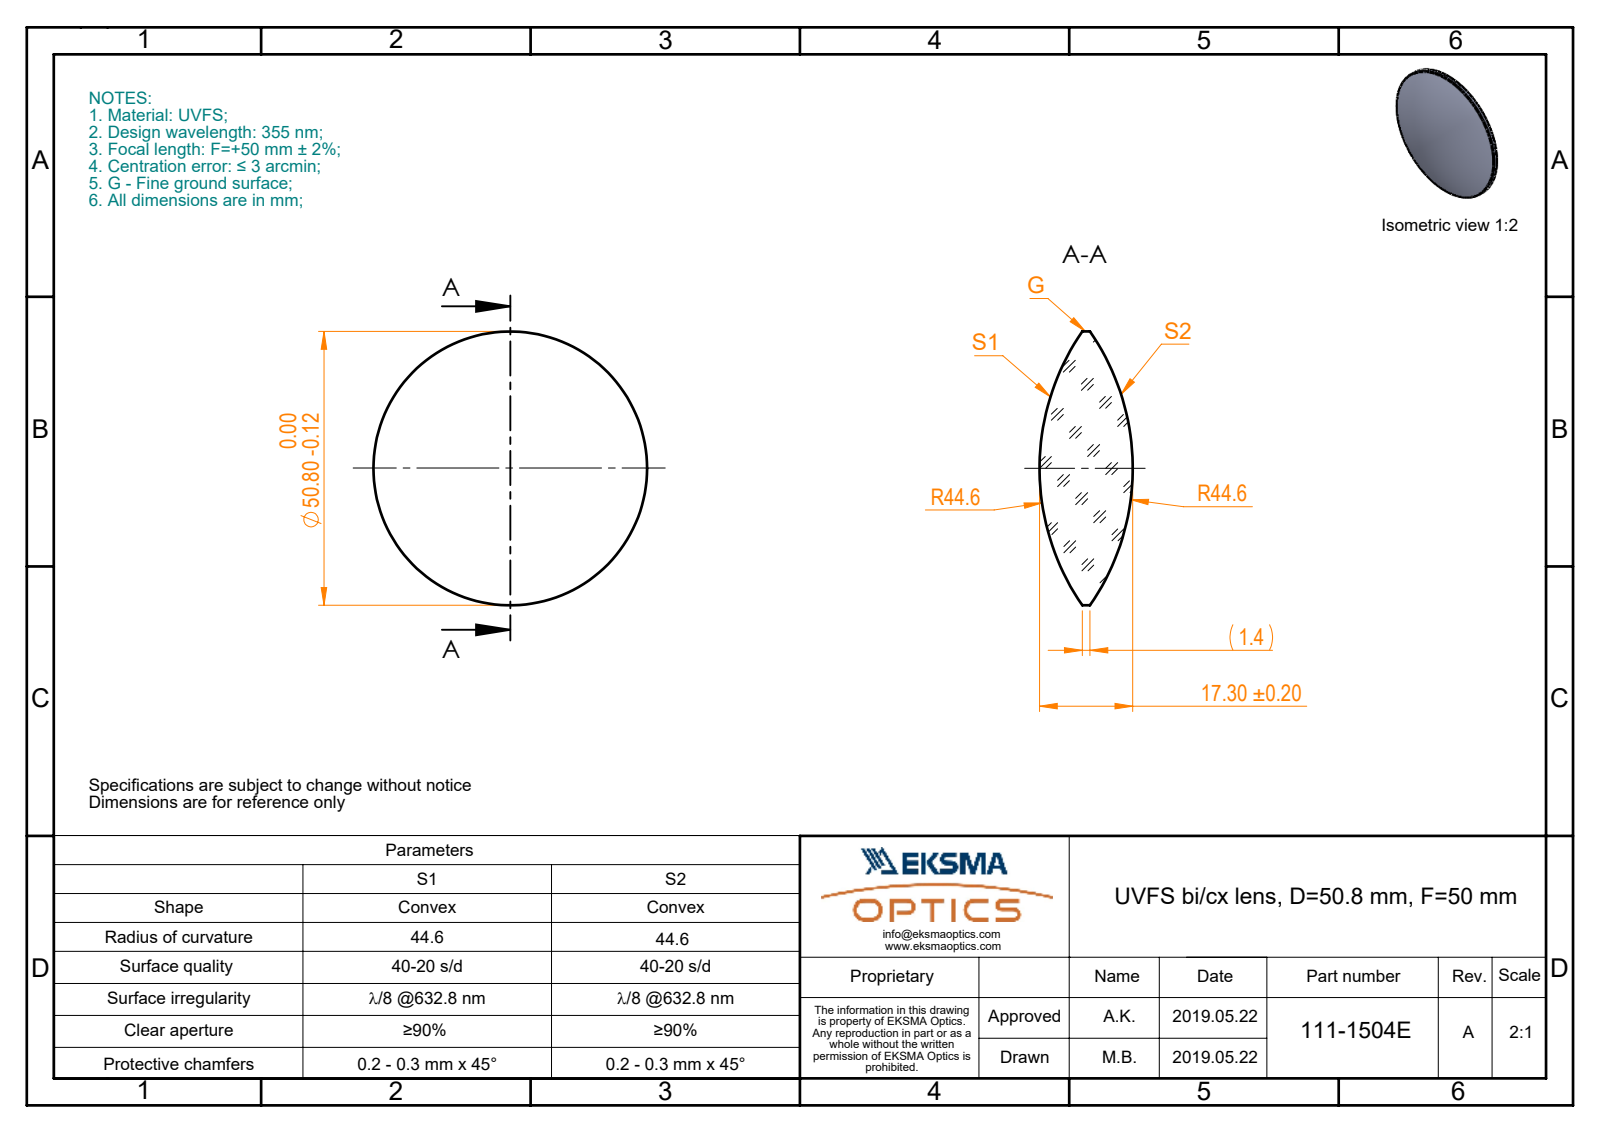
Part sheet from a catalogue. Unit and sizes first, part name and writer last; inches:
Units: inches
Overall size (bounding box): 2 × 2 × 0.681
Round bosses / shafts (diameter × count): ⌀2 ×1
Volume: 1.19 in³ · Surface area: 7.251 in²
Bodies: 1 solid, 6 faces (0 planar, 2 cylindrical, 4 other)
Part name (STEP PRODUCT): 111-1504E UVFS bi-cx 50.8 F50
STEP written by: SolidWorks 2017 (CONFIG_CONTROL_DESIGN)
